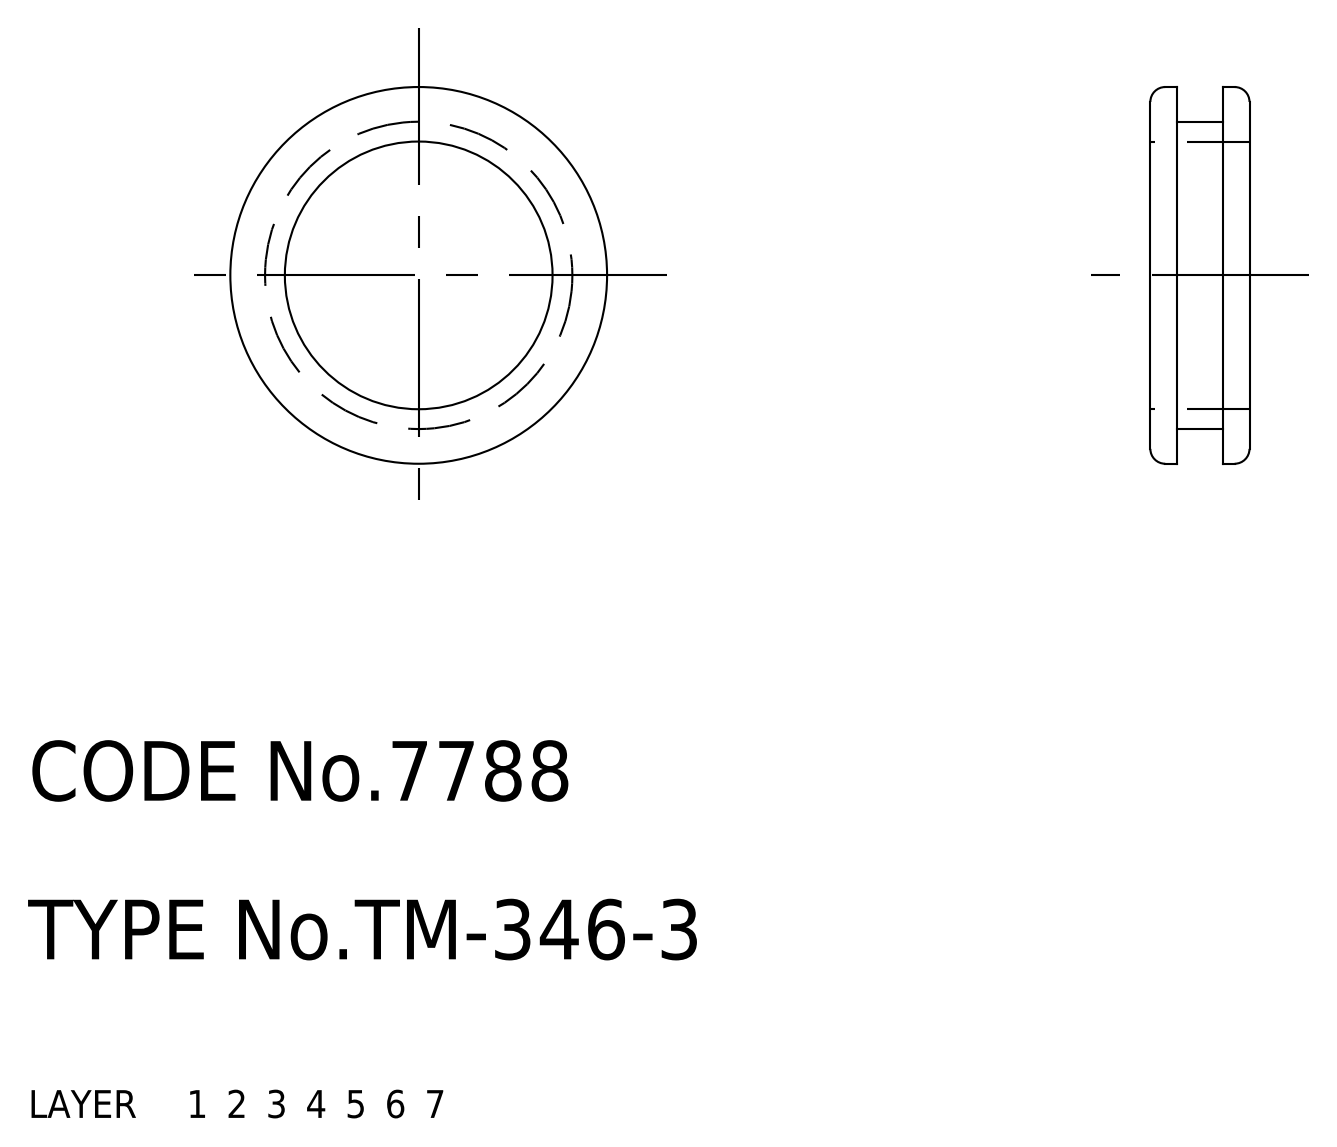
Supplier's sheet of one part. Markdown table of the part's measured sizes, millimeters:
| quantity | value |
| --- | --- |
| part name | TM_346_3 |
| STEP written by | SolidWorks 2015 (AUTOMOTIVE_DESIGN) |
| units | millimeters |
| bodies | 1 solid, 16 faces (4 planar, 8 cylindrical, 4 other) |
| overall size | 19 × 19 × 5 |
| volume | 470 mm³ |
| surface area | 917 mm² |
| round holes (diameter × count) | 13.5 × 1 |
| round bosses / shafts (diameter × count) | 19 × 1, 15.5 × 1 |
| main face-to-face distances | 1.35, 3.65, 5, 2.3 |
